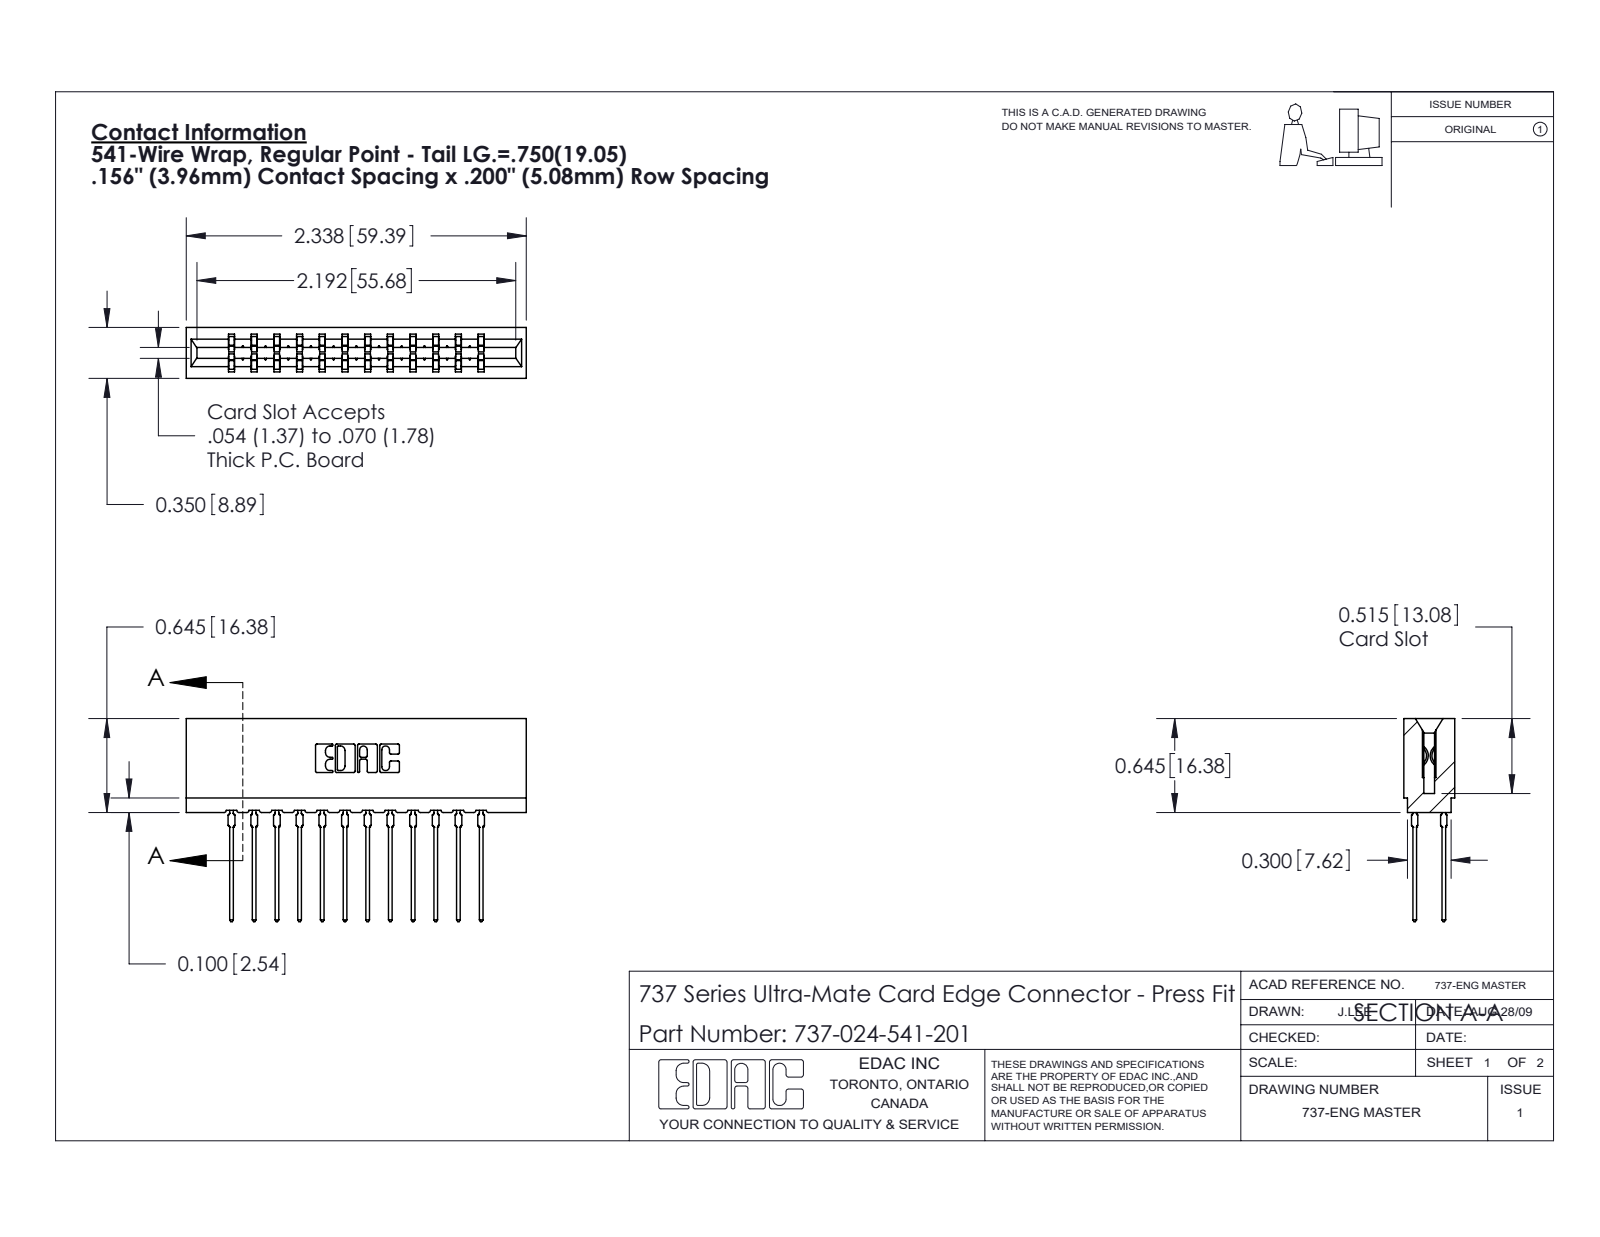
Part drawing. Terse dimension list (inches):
name: 737 Part_Insulator Option - 01; 745-292-001_541; 737-024-541-201
written by: SolidWorks 2020 (CONFIG_CONTROL_DESIGN)
unit: in
bodies: 25 solids, 2254 faces (1170 planar, 460 cylindrical, 624 other)
size: 2.338 × 1.396 × 0.35
volume: 0.377 in³; area: 13.72 in²
rounds: 48× R0.021, 24× R0.015, 22× R0.01, 8× R0.005, 8× R0.011, 6× R0.007, 6× R0.031, 3× R0.026
face distances: 0.138, 0.212, 0.156, 0.35, 0.624, 0.063, 0.287, 0.076, 0.149, 0.312
